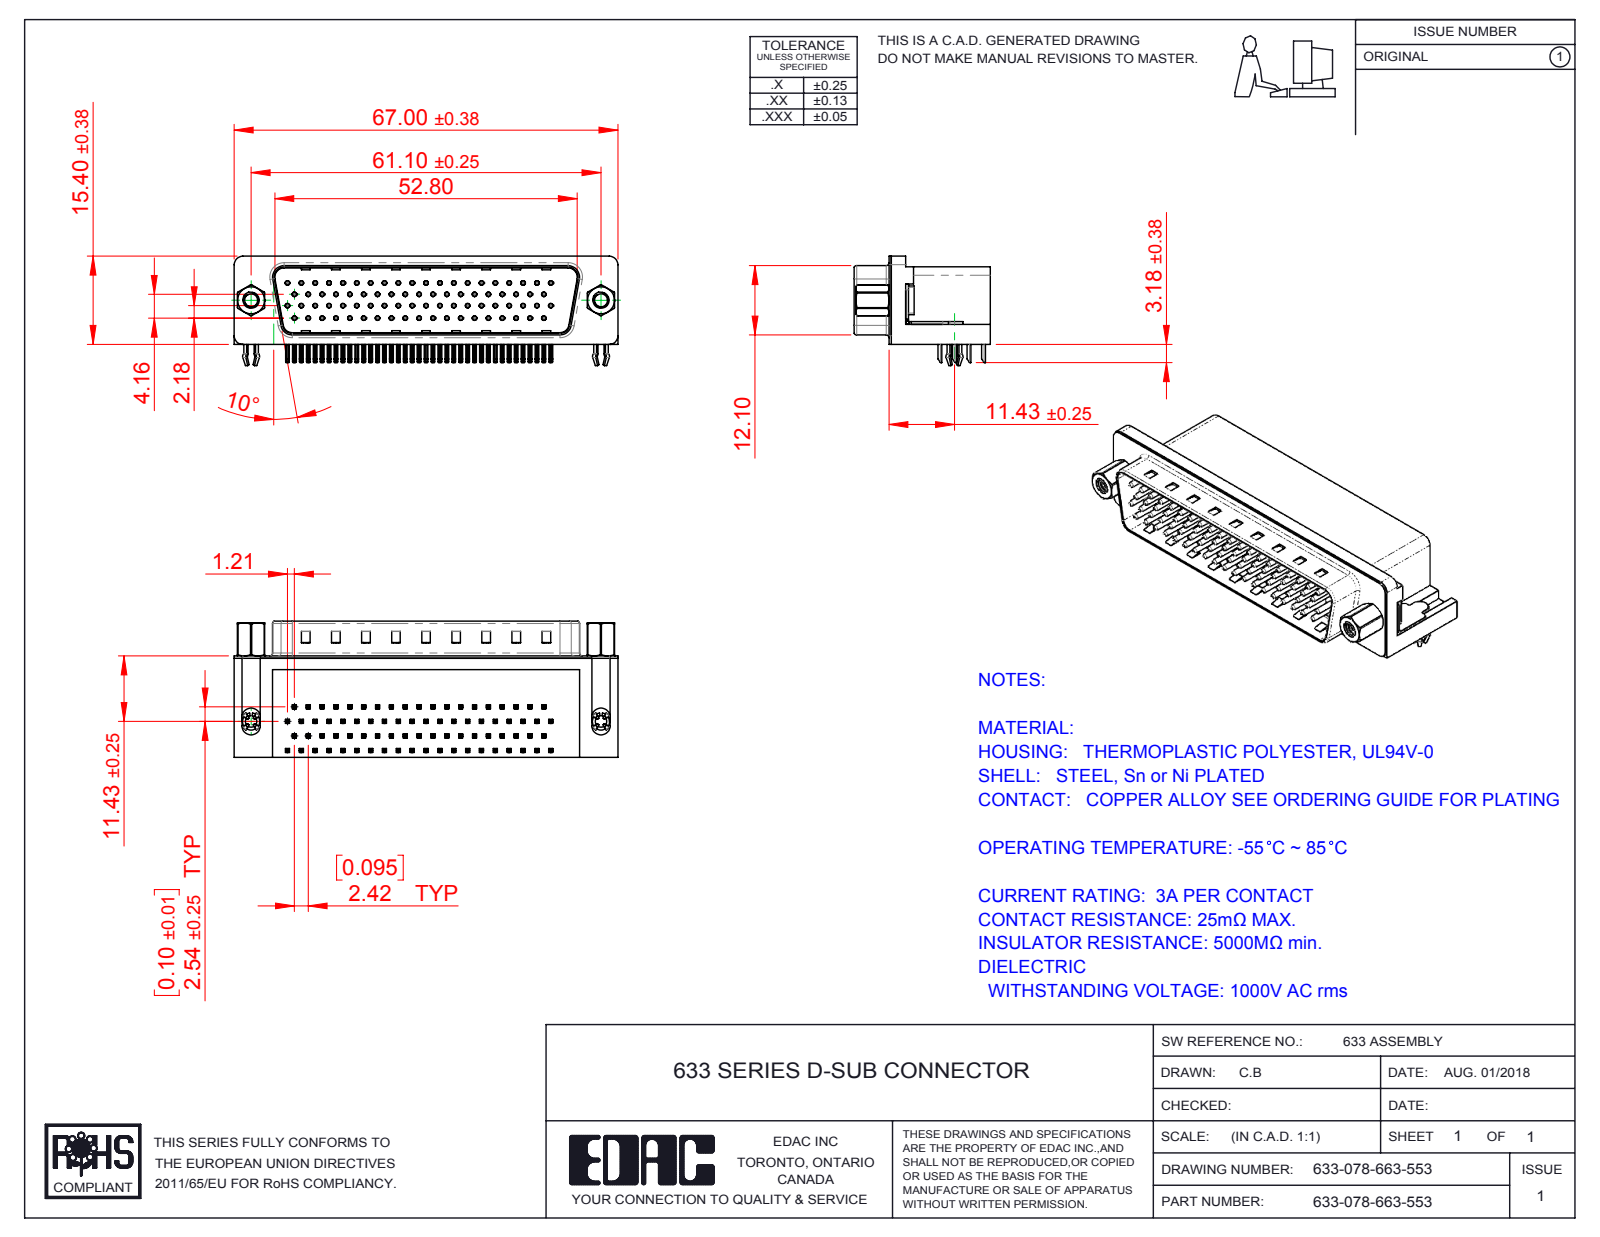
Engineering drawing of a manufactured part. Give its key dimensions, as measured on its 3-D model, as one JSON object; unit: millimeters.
{"part_name": "633-078-663-553; 633 4-40 Threaded Rivet; 633 4 Prong Board Lock_78 Contact; 633 4-40 Hex Standoff (+6 more)", "step_written_by": "SolidWorks 2016 (CONFIG_CONTROL_DESIGN)", "units": "millimeters", "bodies": {"solids": 86, "faces": 6516, "planar": 4045, "cylindrical": 1848, "other": 623}, "overall_size": [67, 23.8, 19.1], "volume_mm3": 14825, "surface_area_mm2": 16882, "round_holes": [[0.35, 78], [0.8, 78], [2, 2], [2.26, 2], [2.29, 2], [4, 2], [4.8, 2], [5, 2]], "round_bosses_or_shafts": [[0.75, 78], [4.9, 2], [4.75, 2], [3.9, 2], [3, 2], [2.79, 2]], "partial_cylinders_radius": [[0.25, 324], [0.12, 156], [1, 16], [0.5, 9], [1.6, 8], [1.5, 6], [0.45, 4], [0.9, 4]], "face_to_face_distances": [0.4, 13.2, 17.3, 11.7, 13.35, 2.05, 13.75, 1.65, 1.85, 11.9], "hole_center_spacings": [2.42, 4.84, 7.26, 9.68, 6.26, 7.13, 12.1, 8.62]}
